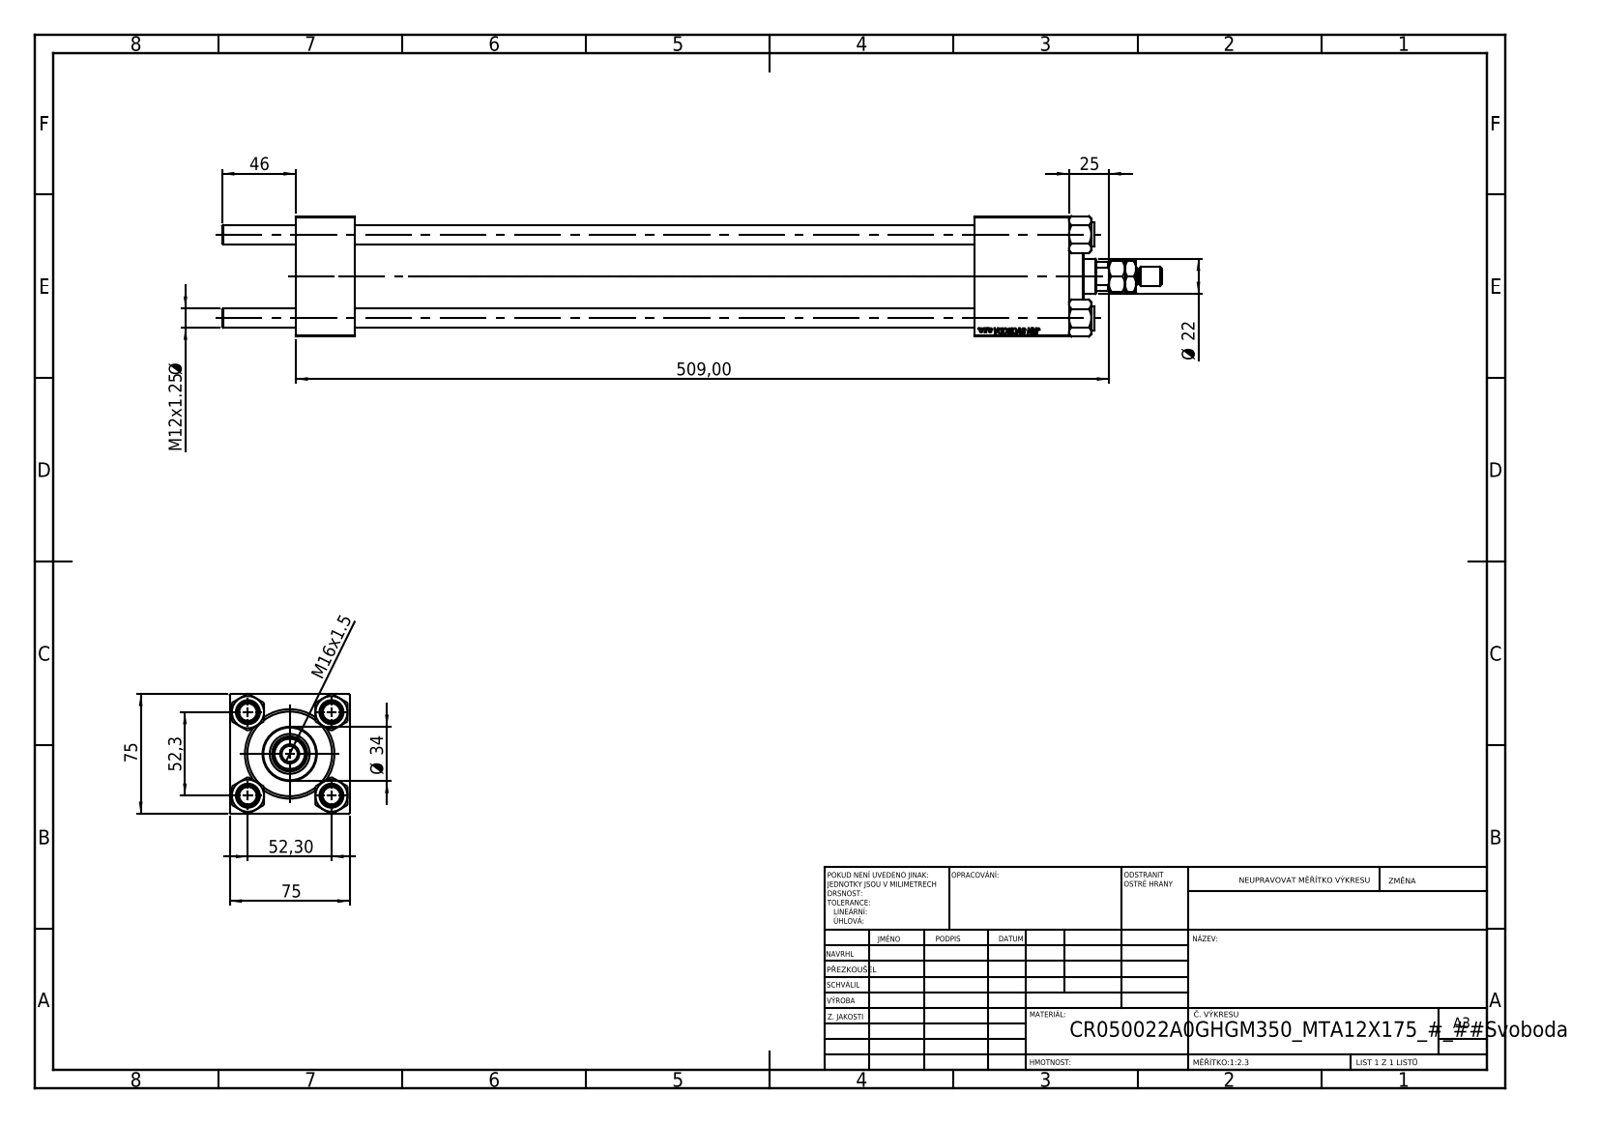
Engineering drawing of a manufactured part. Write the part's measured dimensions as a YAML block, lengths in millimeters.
part_name: "MTA; CR025_012_A_0_G_A_G_M_020_+#_##_TYCINKA; V215CR_BODY_A; V215CR_VCP (+2 more)"
step_written_by: "SolidWorks 2019 (CONFIG_CONTROL_DESIGN)"
units: millimeters
bodies: {solids: 12, faces: 1183, planar: 535, cylindrical: 82, other: 566}
overall_size: [588, 75.54, 75]
volume: 1137000
surface_area: 348524
round_holes:
  - {diameter: 12, count: 4}
  - {diameter: 7, count: 2}
  - {diameter: 20.96, count: 2}
  - {diameter: 30, count: 2}
  - {diameter: 10.5, count: 1}
  - {diameter: 22, count: 1}
  - {diameter: 25, count: 1}
  - {diameter: 41, count: 1}
  - {diameter: 50, count: 1}
  - {diameter: 53, count: 1}
round_bosses_or_shafts:
  - {diameter: 15, count: 4}
  - {diameter: 56, count: 1}
  - {diameter: 34, count: 1}
  - {diameter: 12, count: 1}
  - {diameter: 10, count: 1}
partial_cylinders:
  - {radius: 10.5, count: 1}
face_to_face_distances: [75, 37, 484, 447, 425, 388, 59, 455.3, 418.3, 30.3]
hole_center_spacings: [36.98, 52.3, 73.96, 423.5]
